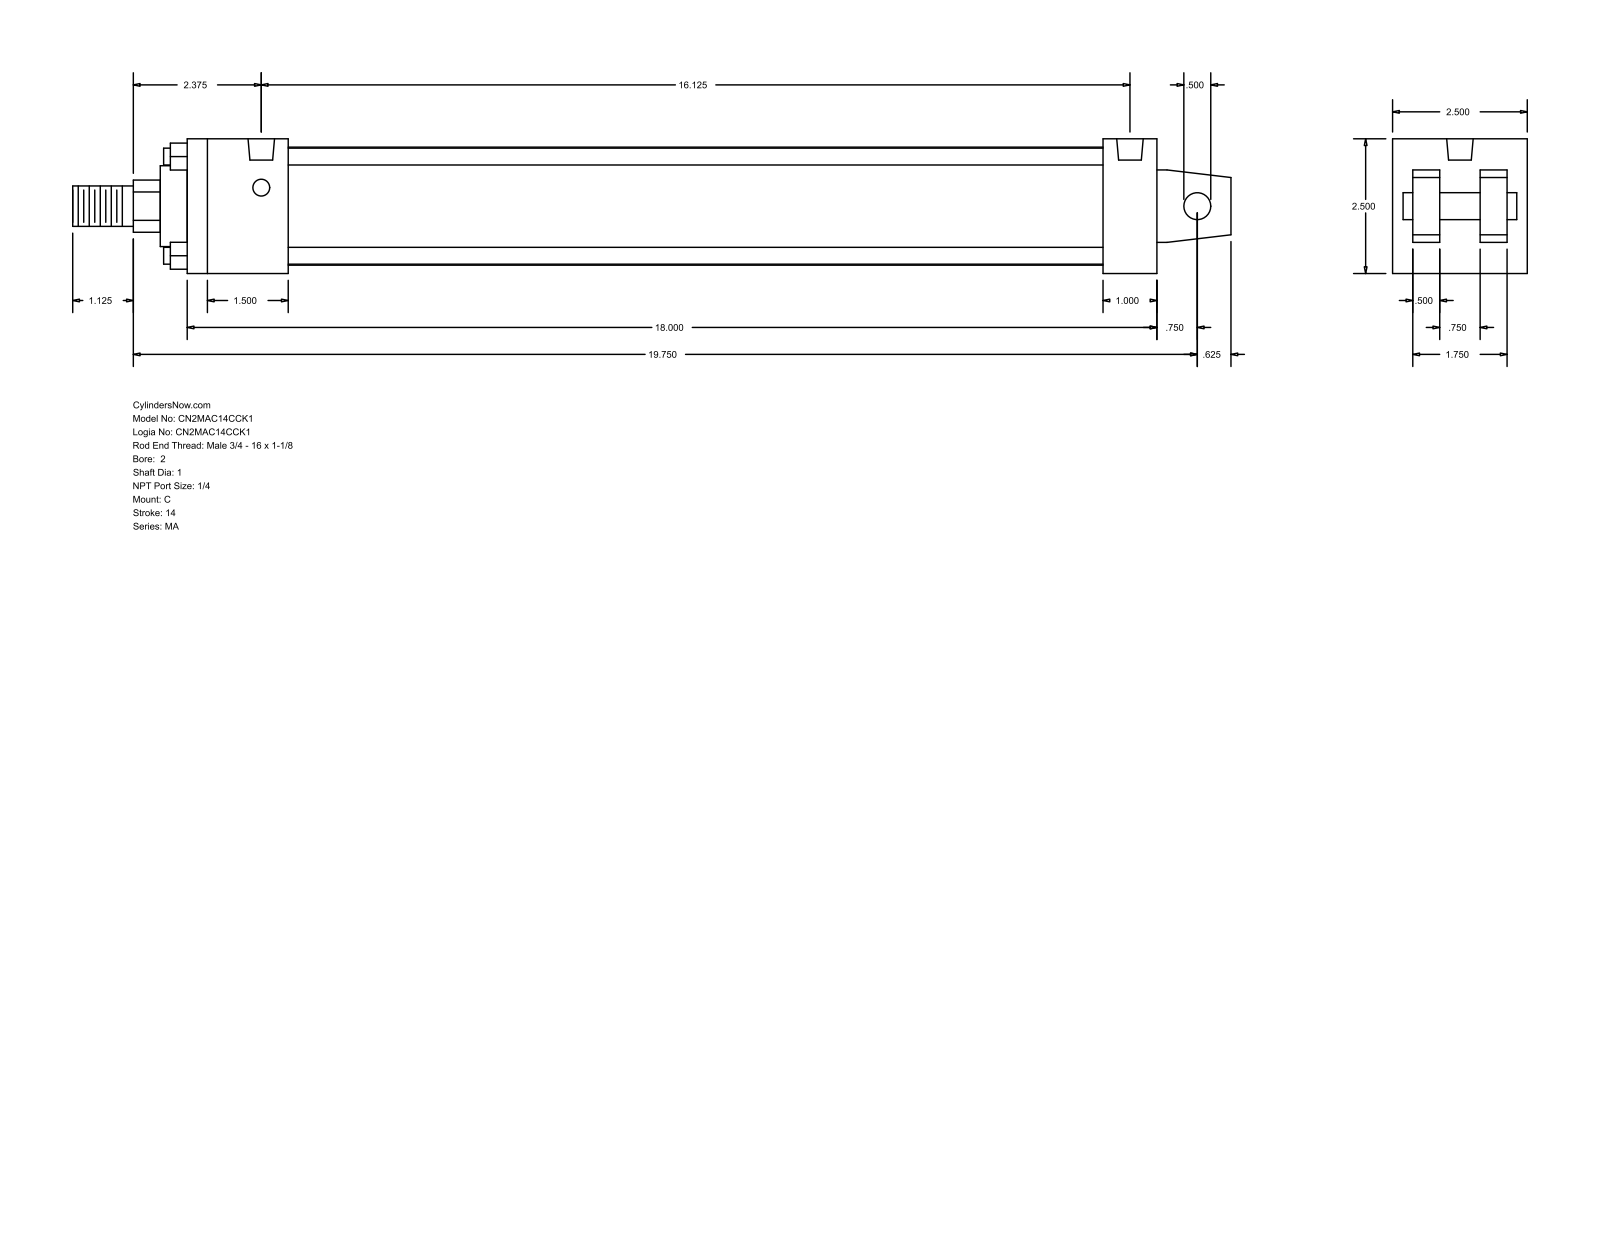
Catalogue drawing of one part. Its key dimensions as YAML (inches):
part_name: "MA_C__0200_1"
step_written_by: "GSSL Pune (CONFIG_CONTROL_DESIGN)"
units: inches
bodies: {solids: 0, faces: 103, planar: 76, cylindrical: 27, other: 0}
overall_size: [21.5, 2.5, 2.5]
round_holes:
  - {diameter: 0.313, count: 4}
  - {diameter: 0.492, count: 2}
round_bosses_or_shafts:
  - {diameter: 0.313, count: 4}
  - {diameter: 2.19, count: 1}
  - {diameter: 1.5, count: 1}
  - {diameter: 1, count: 1}
  - {diameter: 0.75, count: 1}
  - {diameter: 0.5, count: 1}
partial_cylinders:
  - {radius: 0.484, count: 1}
face_to_face_distances: [2.5, 0.5, 18, 0.875, 1.625, 0.375, 2.125, 1.25, 1.875, 1]
hole_center_spacings: [16.125]
